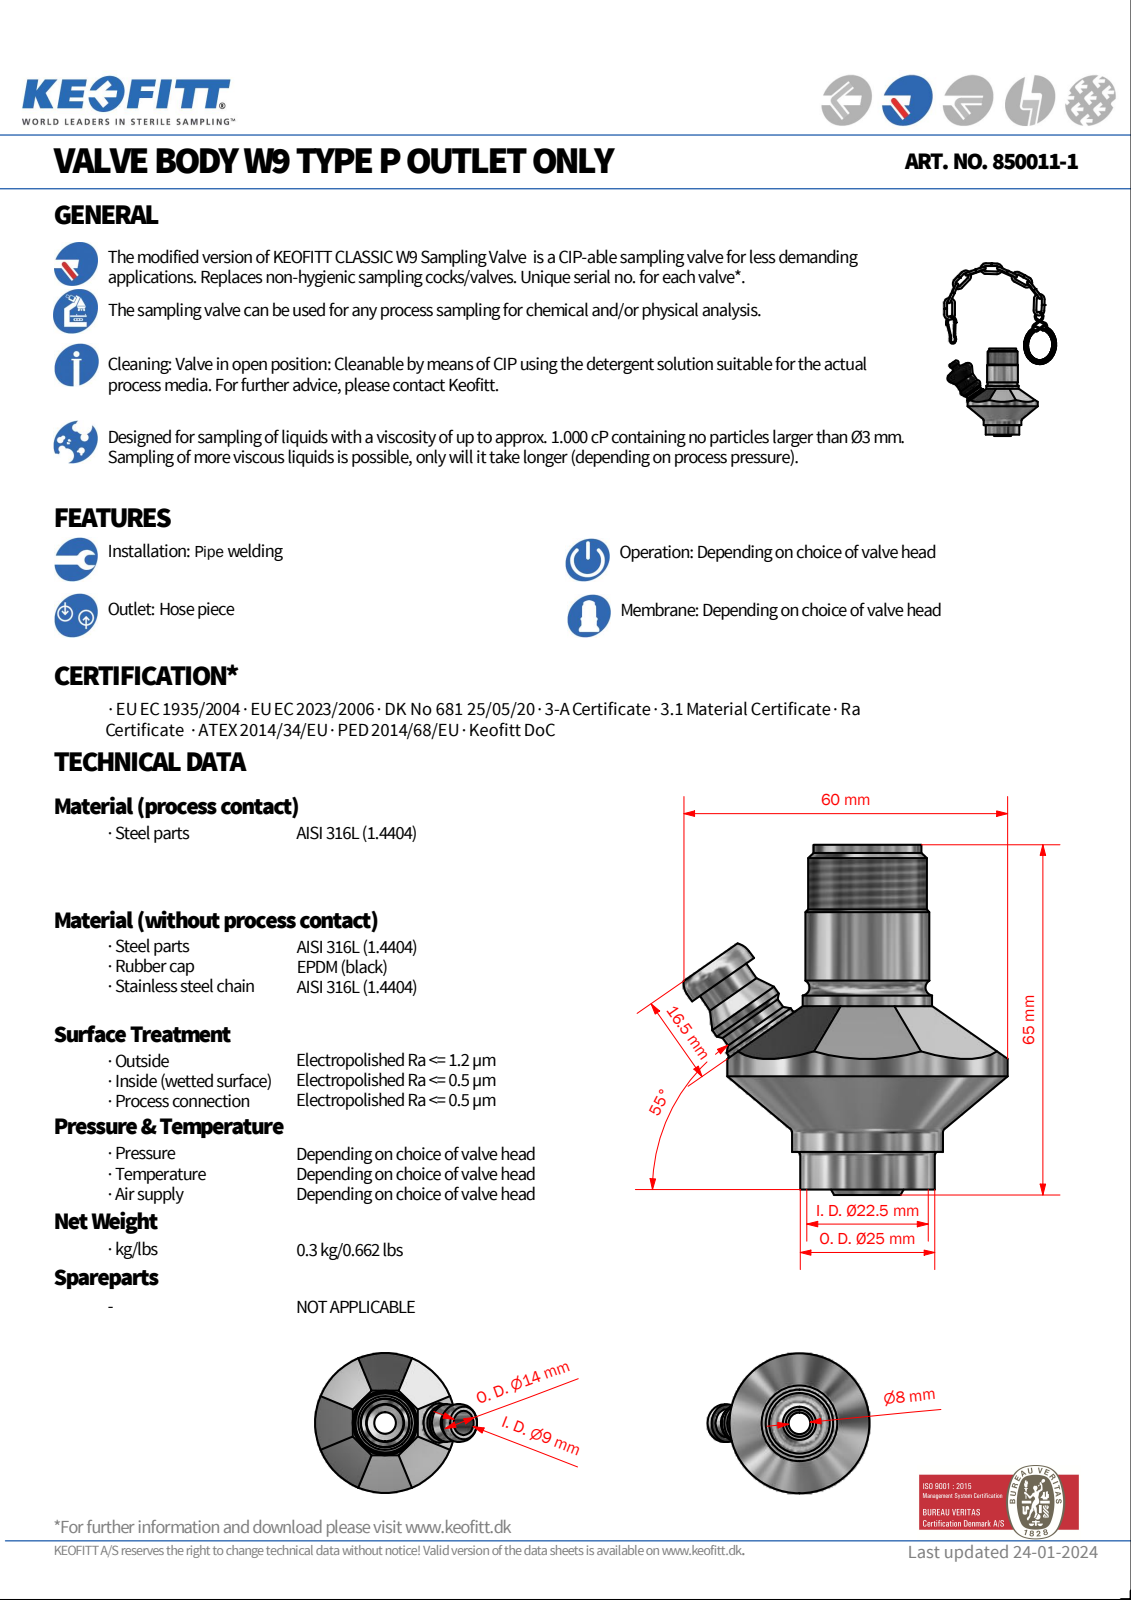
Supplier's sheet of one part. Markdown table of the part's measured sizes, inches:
| quantity | value |
| --- | --- |
| part name | 850011-1 |
| STEP written by | Autodesk Inventor 2022 (AUTOMOTIVE_DESIGN) |
| units | inches |
| bodies | 1 solid, 47 faces (15 planar, 12 cylindrical, 20 other) |
| overall size | 2.559 × 2.367 × 2.047 |
| volume | 3.157 in³ |
| surface area | 14.5 in² |
| round bosses / shafts (diameter × count) | 2.047 × 1, 1.102 × 1, 0.984 × 1, 0.945 × 1, 0.906 × 1, 0.866 × 1, 0.787 × 1, 0.551 × 1 |
| main face-to-face distances | 2.52, 0.039, 2.559, 0.65, 0.492, 0.157, 1.378, 1.339, 1.181, 0.394 |
